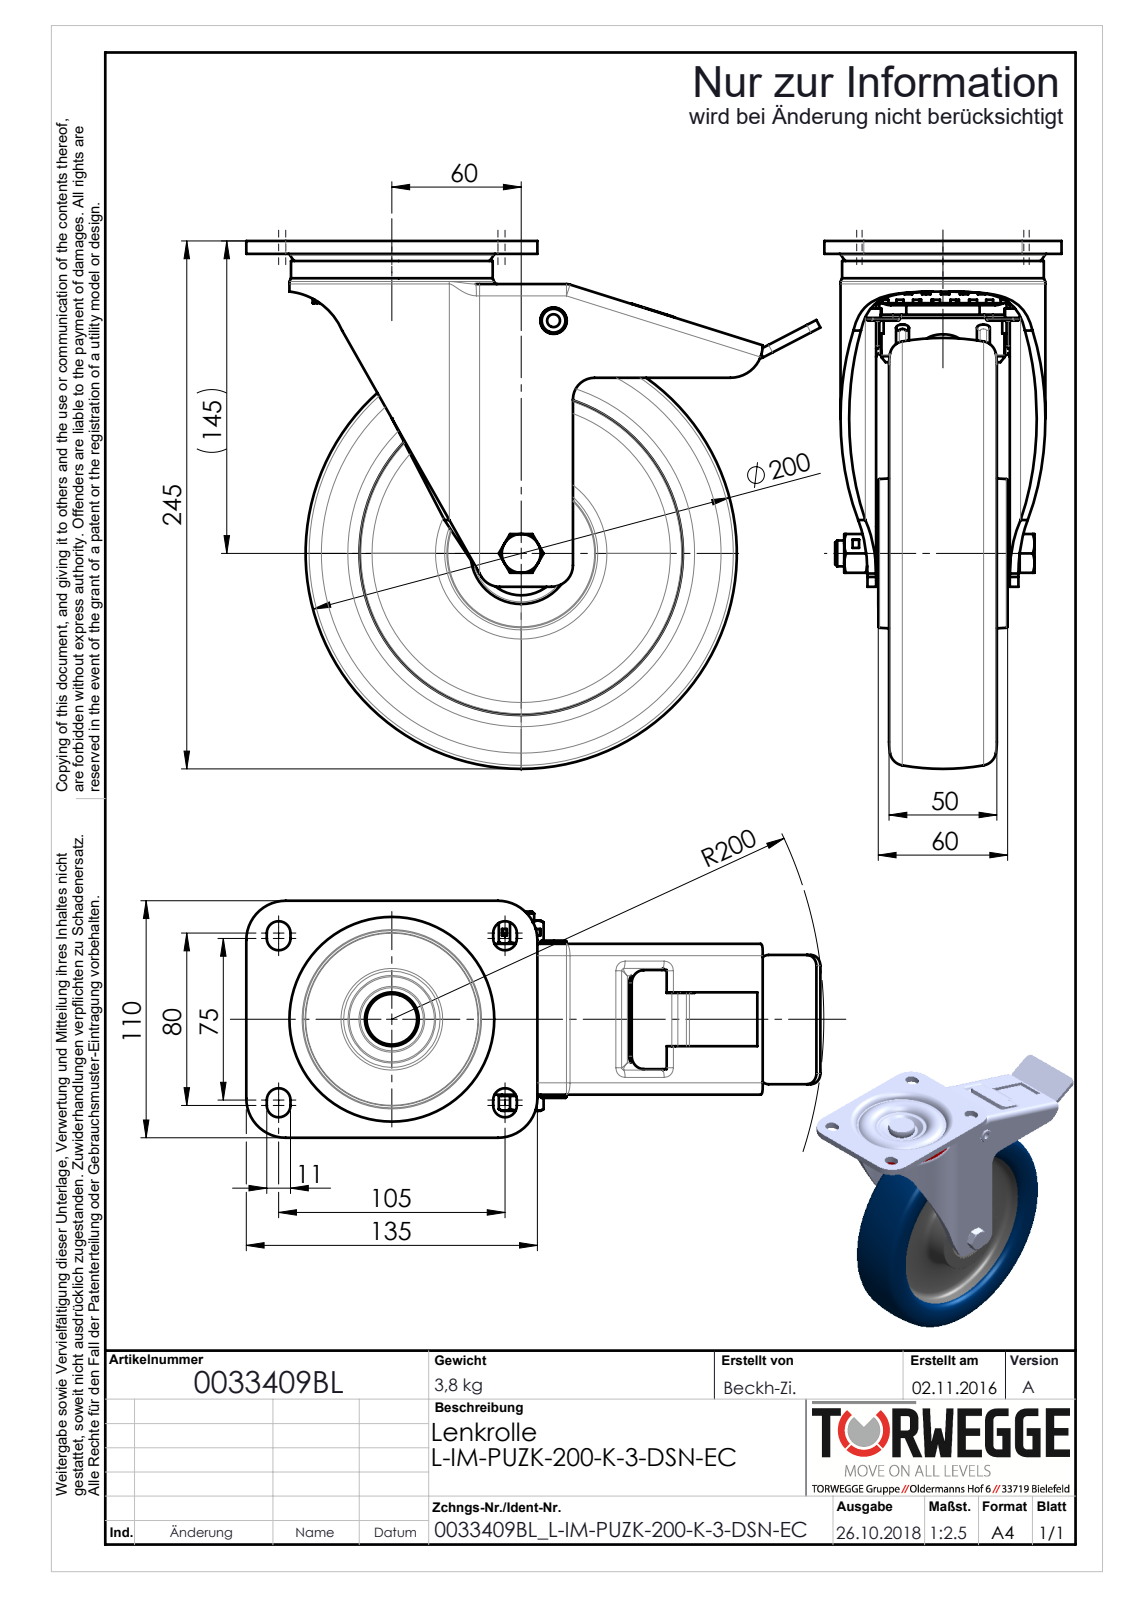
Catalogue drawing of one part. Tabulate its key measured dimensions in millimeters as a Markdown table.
| quantity | value |
| --- | --- |
| part name | 0033409_L-IM-PUZK-200-K-3-DSN-EC |
| STEP written by | SolidWorks 2016 (AUTOMOTIVE_DESIGN) |
| units | millimeters |
| bodies | 0 solids, 574 faces (263 planar, 140 cylindrical, 171 other) |
| overall size | 266.25 × 245 × 110 |
| round holes (diameter × count) | 3.6 × 1, 6 × 1, 9.6 × 1, 12.3 × 1, 12.6 × 1, 15.6 × 1 |
| round bosses / shafts (diameter × count) | 18 × 2, 12 × 2, 8 × 2, 93.54 × 1, 73.32 × 1, 21.94 × 1, 17 × 1, 14 × 1 |
| partial cylindrical surfaces (radius × count) | 5.5 × 13, 4 × 8, 5 × 8, 1.5 × 7, 0.75 × 4, 18.29 × 4, 10 × 3, 29 × 3 |
| main face-to-face distances | 4, 66, 62, 70, 6, 20, 24, 1.5, 18, 2.78 |
